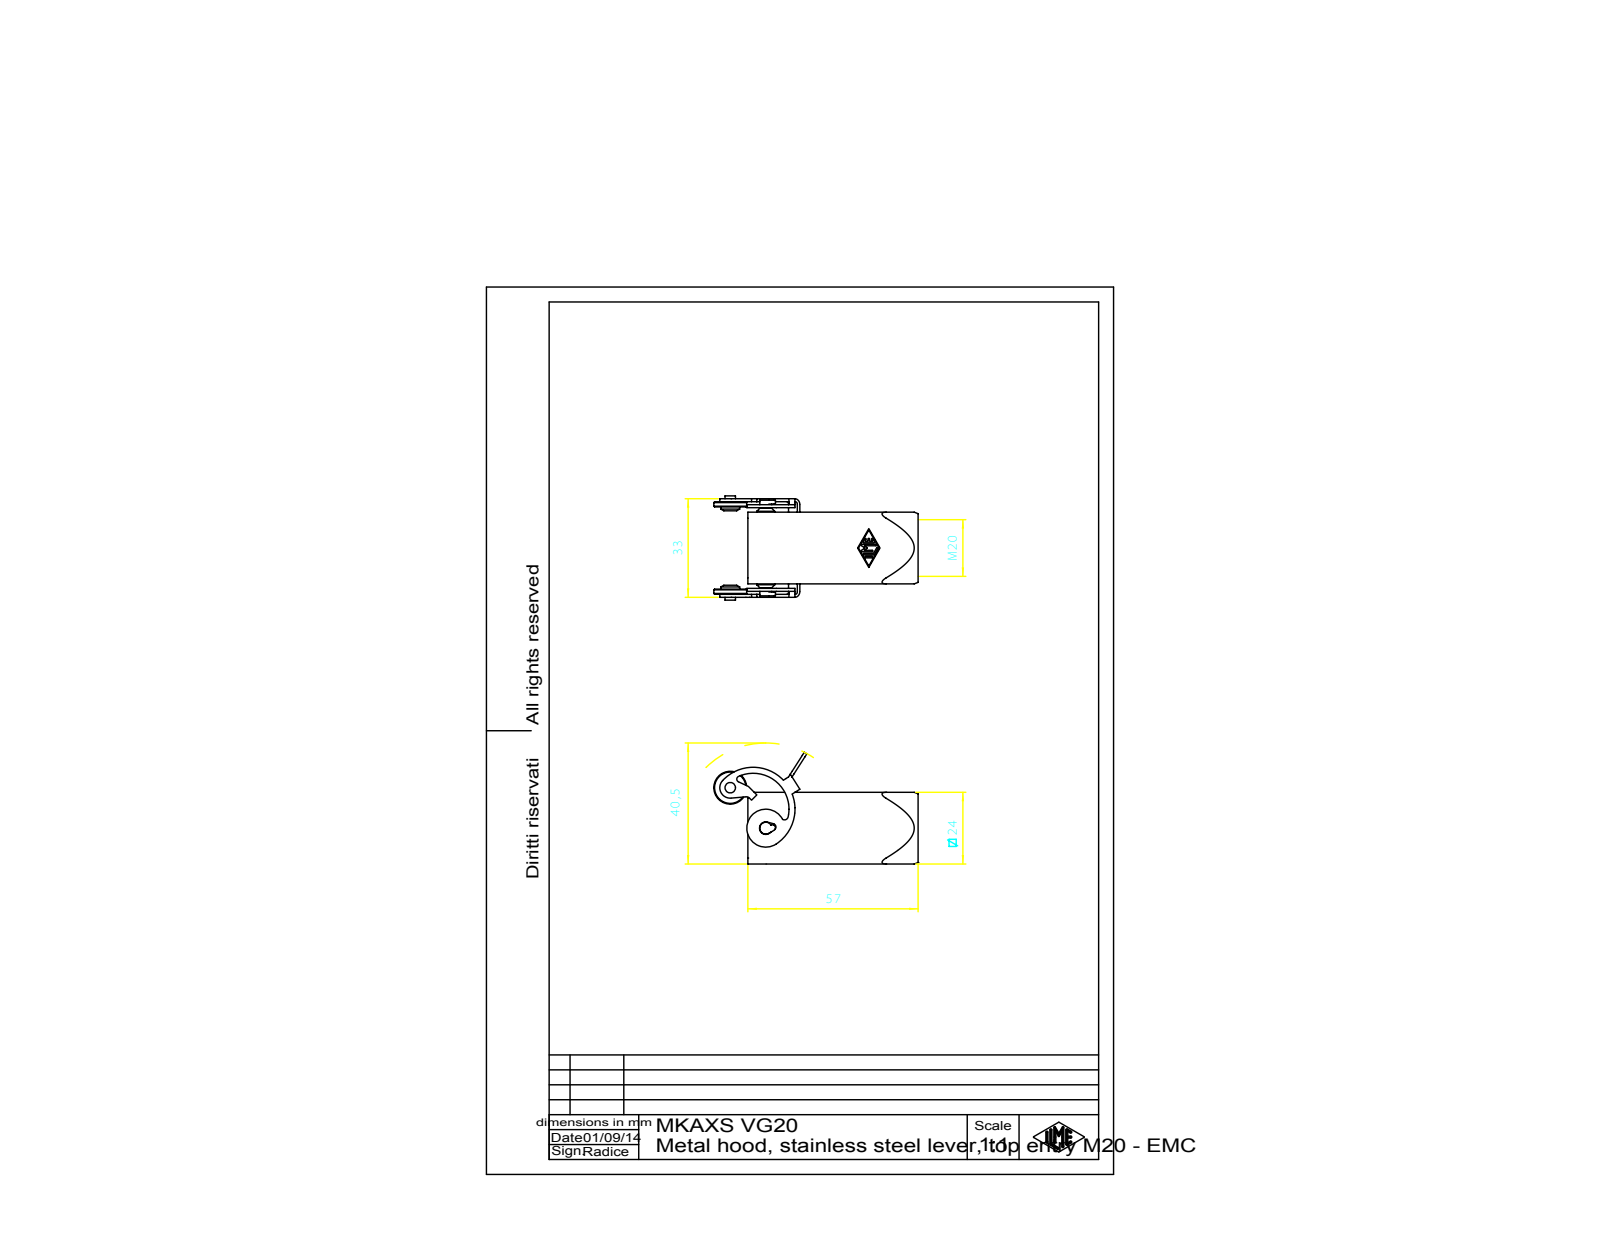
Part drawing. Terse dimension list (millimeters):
name: MKAXS VG20
written by: Autodesk Inventor 7 (AUTOMOTIVE_DESIGN)
unit: mm
bodies: 2 solids, 237 faces (81 planar, 90 cylindrical, 66 other)
size: 62.9 × 37.42 × 34.9
volume: 7 963 mm³; area: 12 199 mm²
holes: 1× ⌀3.3, 1× ⌀15, 1× ⌀20
bosses: 1× ⌀11, 1× ⌀6.3, 1× ⌀6, 1× ⌀4, 1× ⌀3.5
rounds: 18× R2, 14× R0.25, 6× R1, 2× R0.8, 1× R1.1, 1× R1.25, 1× R1.5, 1× R2.1
face distances: 1, 23, 24, 22, 2, 3, 2.5, 25.5, 3.5, 26.5
